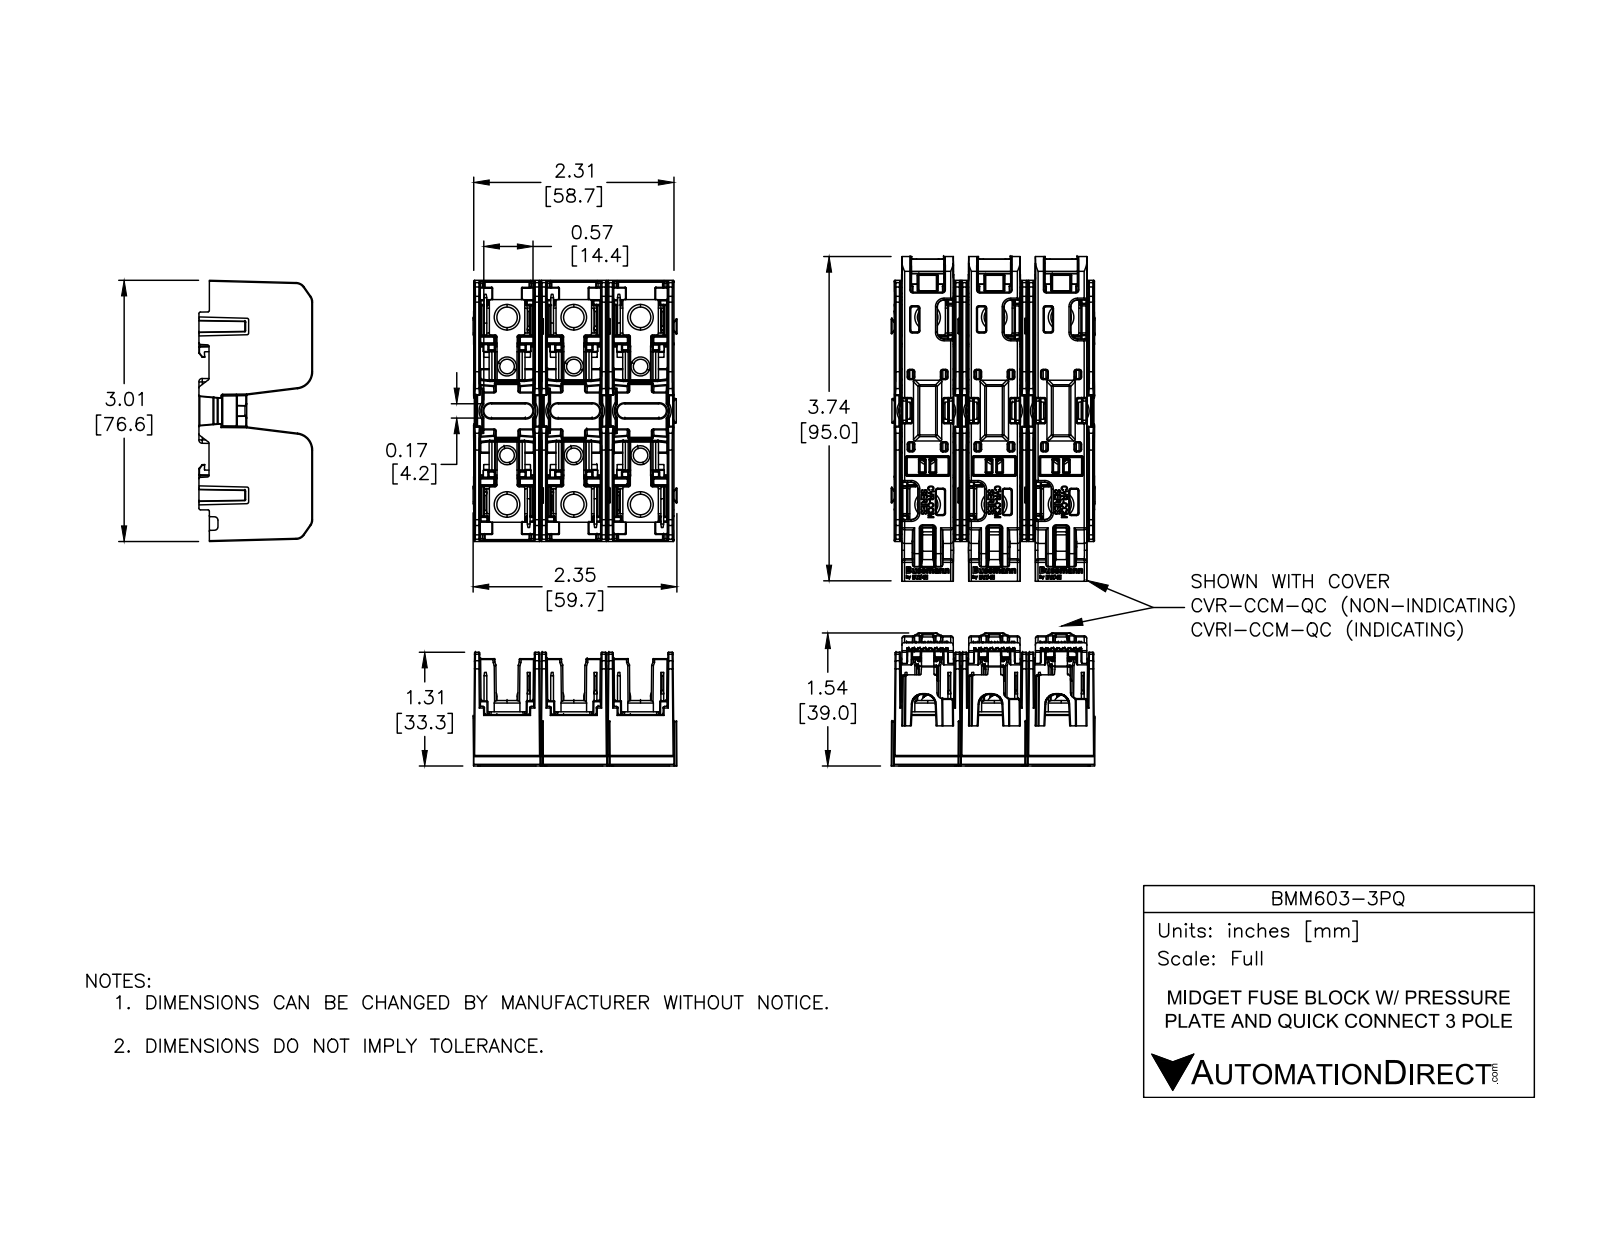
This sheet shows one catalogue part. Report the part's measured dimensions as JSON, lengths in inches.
{"part_name": "BMM603-3PQ", "step_written_by": "SolidWorks 2021 (CONFIG_CONTROL_DESIGN)", "units": "inches", "bodies": {"solids": 13, "faces": 1461, "planar": 1026, "cylindrical": 277, "other": 158}, "overall_size": [3.015, 2.346, 1.312], "volume_in3": 3.718, "surface_area_in2": 77.69, "round_holes": [[0.142, 6], [0.075, 4]], "round_bosses_or_shafts": [[0.295, 6], [0.22, 4], [0.138, 4]], "partial_cylinders_radius": [[0.004, 36], [0.02, 36], [0.03, 6], [0.053, 6], [0.061, 6], [0.084, 6], [0.085, 6], [0.175, 6]], "face_to_face_distances": [0.768, 1.535, 0.691, 0.691, 0.594, 0.077, 0.077, 1.458, 1.459, 0.032], "hole_center_spacings": [0.768, 1.281, 1.025, 0.119, 1.535, 1.846, 2.232, 2.124]}
